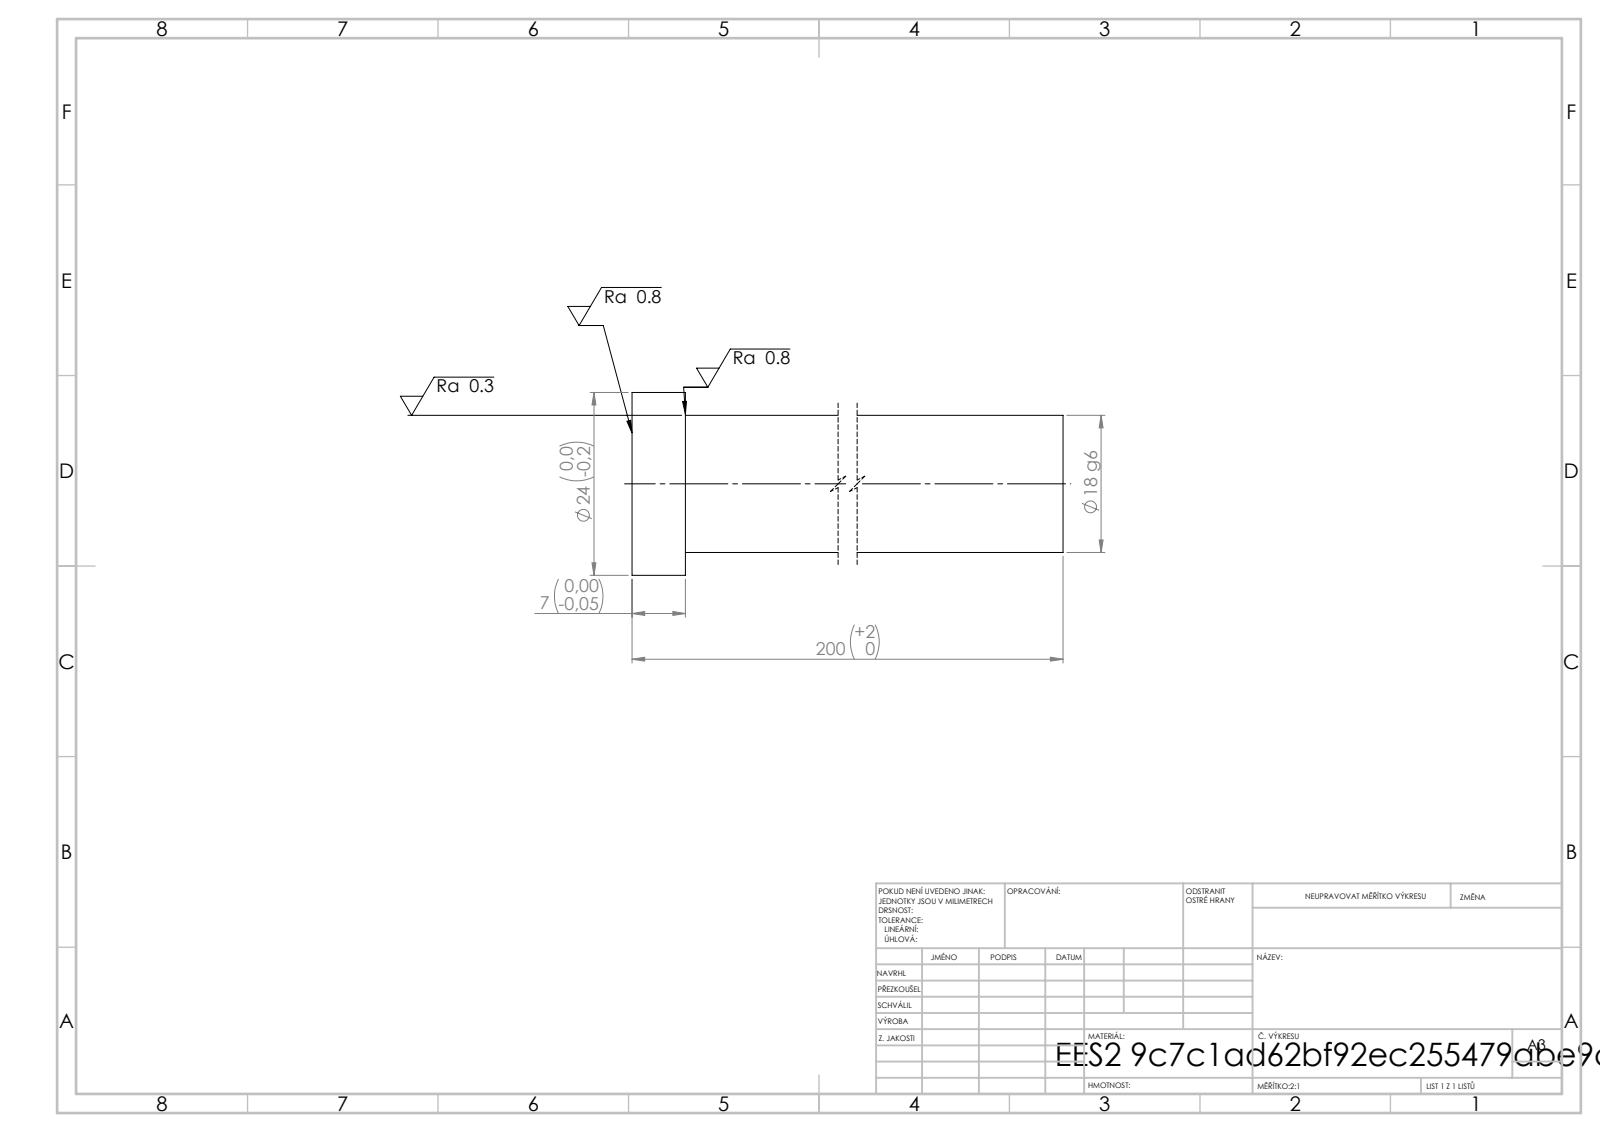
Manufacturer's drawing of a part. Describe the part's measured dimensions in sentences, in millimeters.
Its 3-D file was written by "SolidWorks 2019 (CONFIG_CONTROL_DESIGN)". It is 1 solid with 7 faces: 3 planar, 4 cylindrical and 0 other. Overall it measures 200 by 24 by 24 millimeters. Its volume is 52 279 cubic millimeters and its surface area 12 346 square millimeters. Round bosses or shafts: 1 of diameter 24, 1 of diameter 18. The main face-to-face distances are 200, 7, 193.
